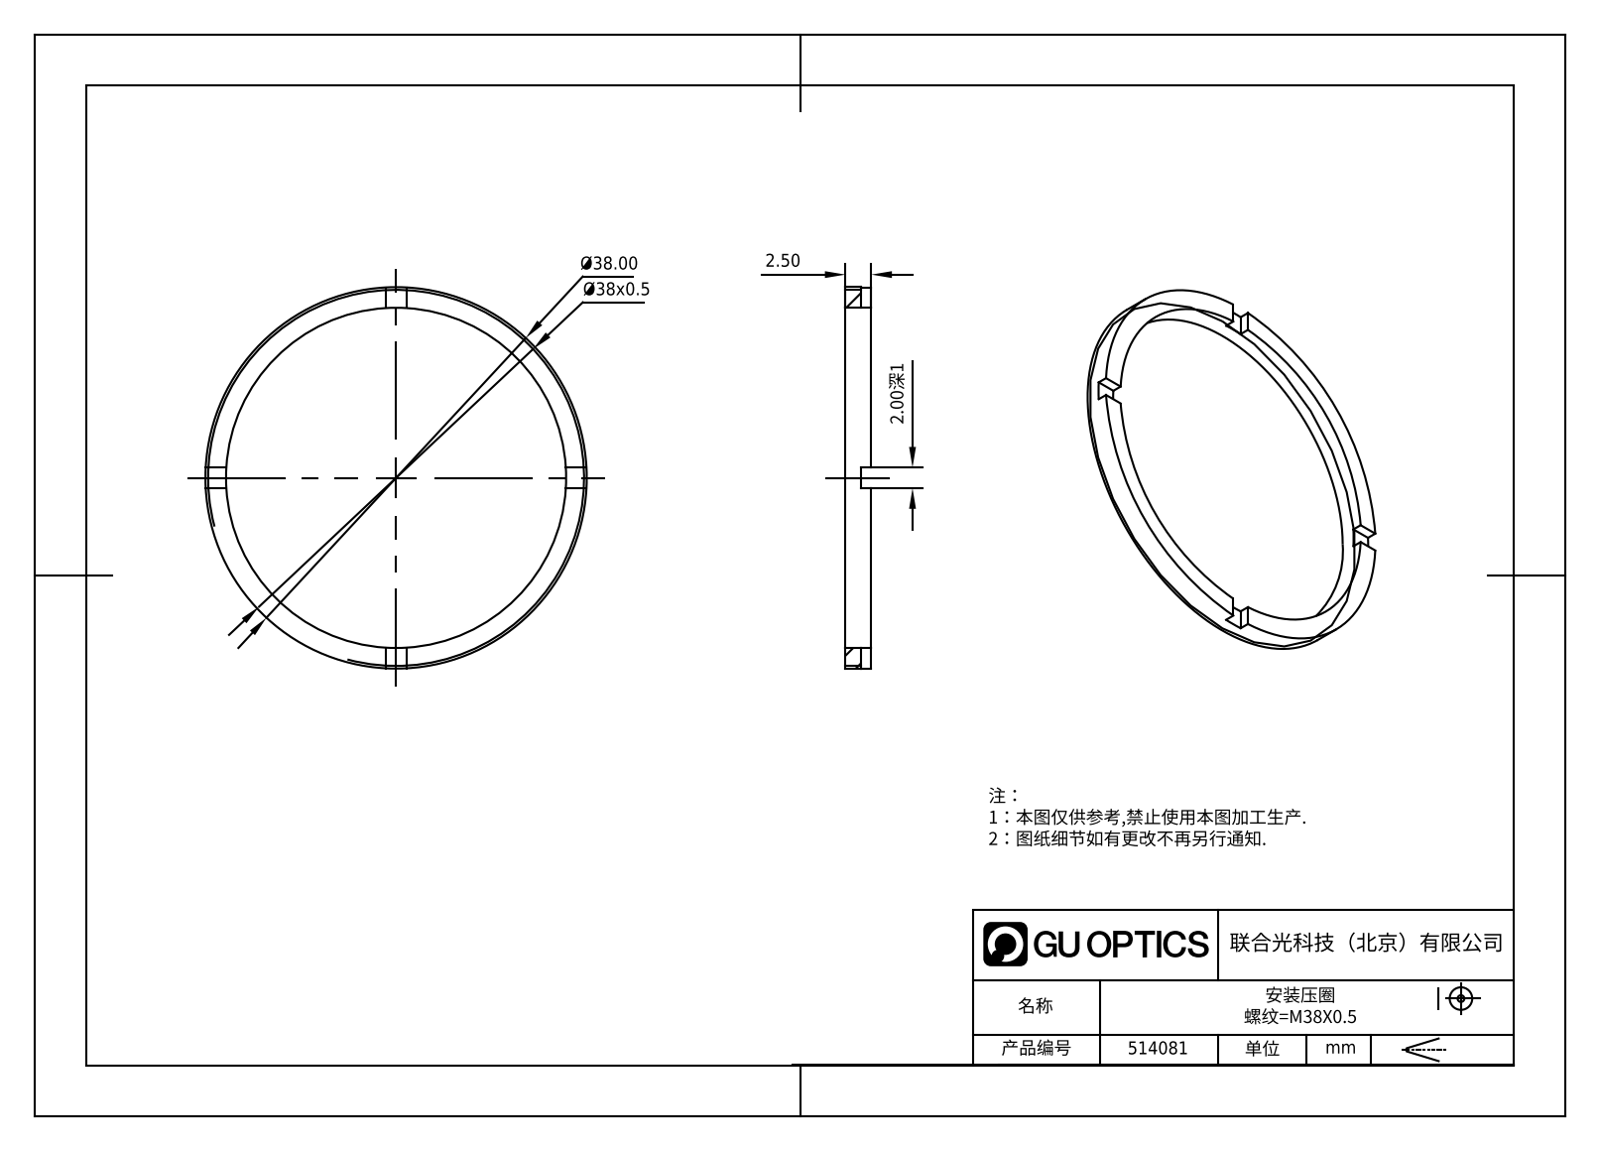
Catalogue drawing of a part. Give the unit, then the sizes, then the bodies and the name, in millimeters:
Units: millimetres
Overall size (bounding box): 38 × 38 × 2.5
Round holes (diameter × count): ⌀34 ×1
Round bosses / shafts (diameter × count): ⌀38 ×1
Main face-to-face distances: 2.5, 1.5, 1, 2
Volume: 549 mm³ · Surface area: 1 018 mm²
Bodies: 1 solid, 21 faces (17 planar, 4 cylindrical, 0 other)
Part name (STEP PRODUCT): 514081
STEP written by: SolidWorks 2020 (CONFIG_CONTROL_DESIGN)
